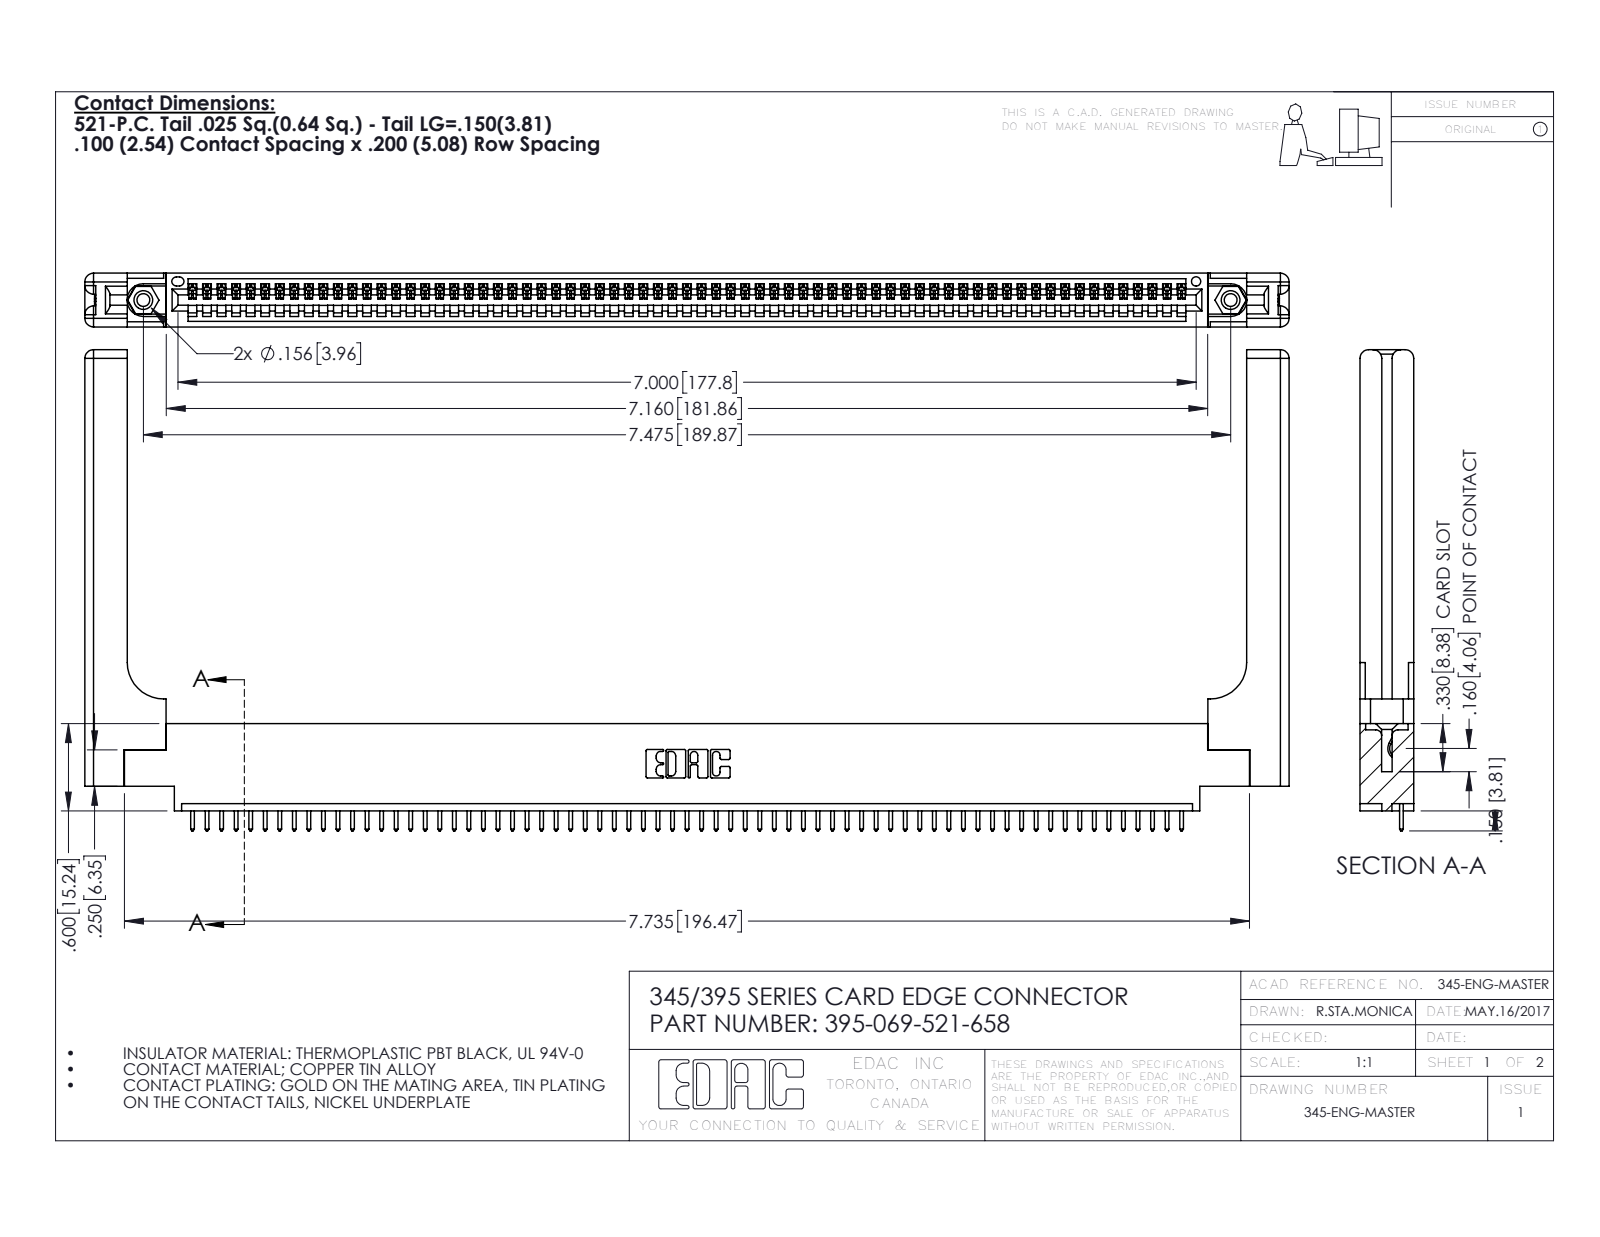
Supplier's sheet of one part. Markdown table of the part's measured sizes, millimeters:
| quantity | value |
| --- | --- |
| part name | 395-069-521-658; 345-250-001_345-250-001-102; 345 Part_0.170 Offset - 0.156 Dia-TH; 345-292-001_345-293-121 (+1 more) |
| STEP written by | SolidWorks 2016 (CONFIG_CONTROL_DESIGN) |
| units | millimeters |
| bodies | 74 solids, 4388 faces (2992 planar, 1336 cylindrical, 60 other) |
| overall size | 210.3 × 84 × 9.4 |
| volume | 28 380 mm³ |
| surface area | 31 460 mm² |
| round holes (diameter × count) | 2.3 × 2, 3.2 × 2, 4 × 2, 1.6 × 1 |
| round bosses / shafts (diameter × count) | 3.9 × 2 |
| partial cylindrical surfaces (radius × count) | 0.2 × 138, 0.3 × 138, 0.3 × 22, 1.5 × 16, 0.2 × 6, 0.8 × 6, 0.7 × 3, 0.8 × 2 |
| main face-to-face distances | 1.8, 9.4, 7.6, 2.5, 6.9, 0.6, 5.1, 5.7, 3.8, 3.8 |
| hole center spacings | 6.9, 183.9, 189.9 |
